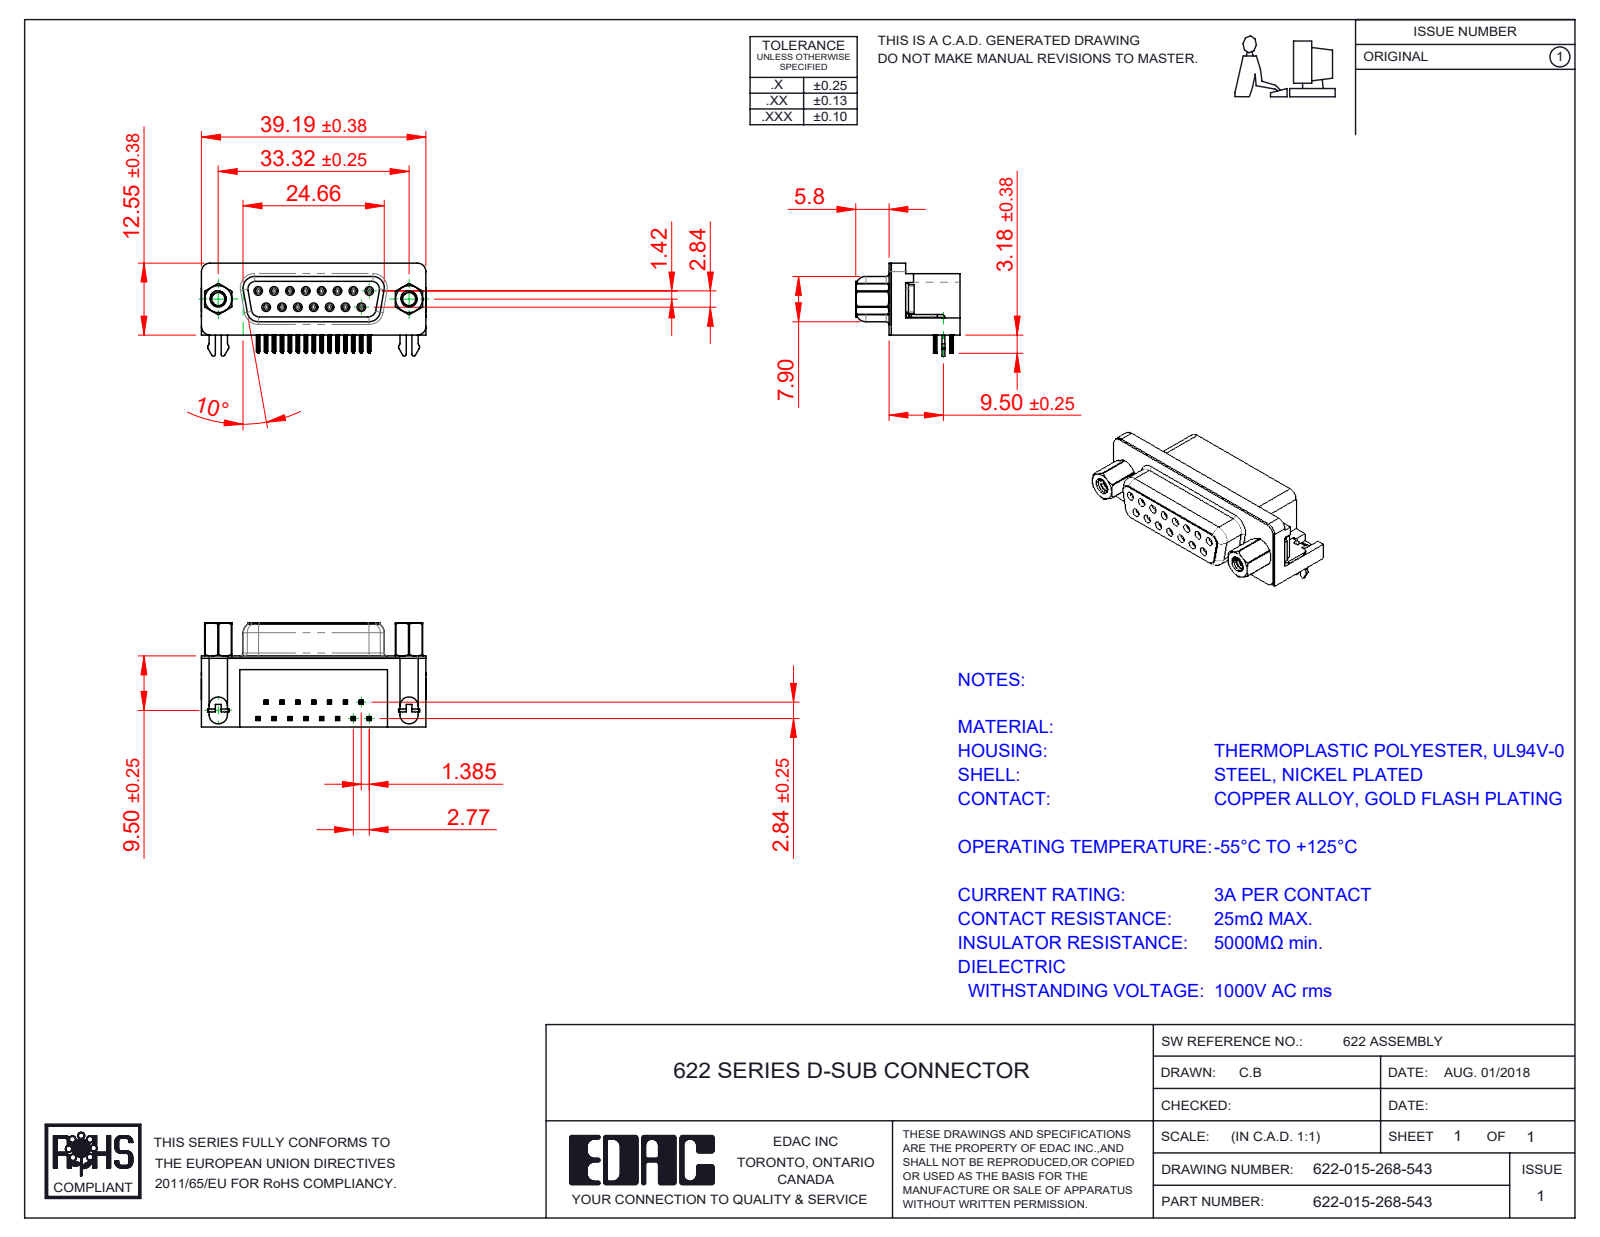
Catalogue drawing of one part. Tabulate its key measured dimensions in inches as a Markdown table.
| quantity | value |
| --- | --- |
| part name | 622 Housing_15 Socket; 622 Contact Top; 622 Shell_15 Socket; 622 4-40 Threaded Rivet (+4 more) |
| STEP written by | SolidWorks 2016 (CONFIG_CONTROL_DESIGN) |
| units | inches |
| bodies | 23 solids, 2667 faces (1138 planar, 675 cylindrical, 854 other) |
| overall size | 1.544 × 0.717 × 0.64 |
| volume | 0.33 in³ |
| surface area | 11.23 in² |
| round holes (diameter × count) | 0.031 × 15, 0.035 × 15, 0.079 × 2, 0.089 × 2, 0.09 × 2, 0.157 × 2, 0.189 × 2, 0.197 × 2 |
| round bosses / shafts (diameter × count) | 0.047 × 15, 0.193 × 2, 0.187 × 2, 0.154 × 2, 0.118 × 2, 0.11 × 2 |
| partial cylindrical surfaces (radius × count) | 0.004 × 120, 0.006 × 60, 0.014 × 30, 0.039 × 18, 0.013 × 15, 0.01 × 12, 0.053 × 8, 0.059 × 8 |
| main face-to-face distances | 0.016, 0.472, 0.244, 0.488, 0.407, 0.114, 0.262, 0.033, 0.014, 0.228 |
| hole center spacings | 0.124, 0.109, 0.218, 0.327, 0.436, 0.198, 0.198, 0.294 |
